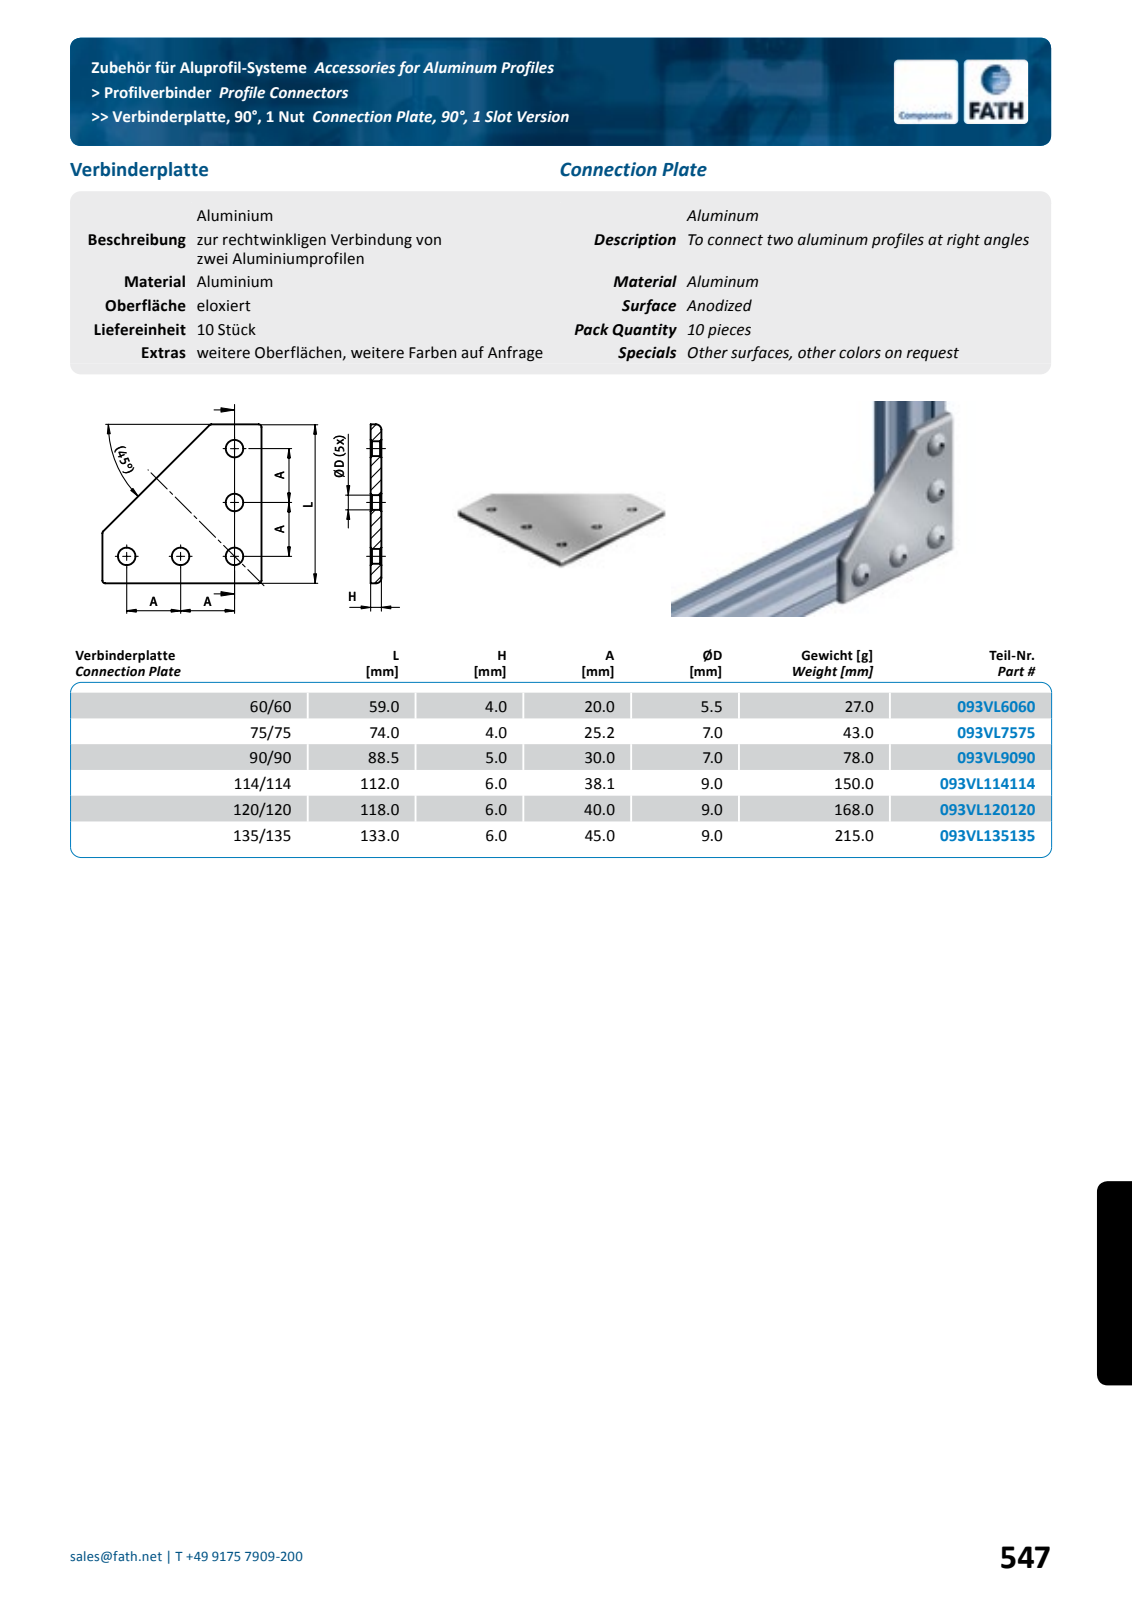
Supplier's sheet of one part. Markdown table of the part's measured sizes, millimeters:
| quantity | value |
| --- | --- |
| part name | fath_093vl120120 |
| STEP written by | Spatial InterOp 3D (automotive_design) |
| units | millimeters |
| bodies | 1 solid, 52 faces (7 planar, 20 cylindrical, 25 other) |
| overall size | 118 × 118 × 6 |
| volume | 62 022 mm³ |
| surface area | 23 745 mm² |
| round holes (diameter × count) | 9 × 5 |
| partial cylindrical surfaces (radius × count) | 2 × 10 |
| main face-to-face distances | 6, 118 |
| hole center spacings | 40, 80, 89.44, 56.57, 113.14 |
